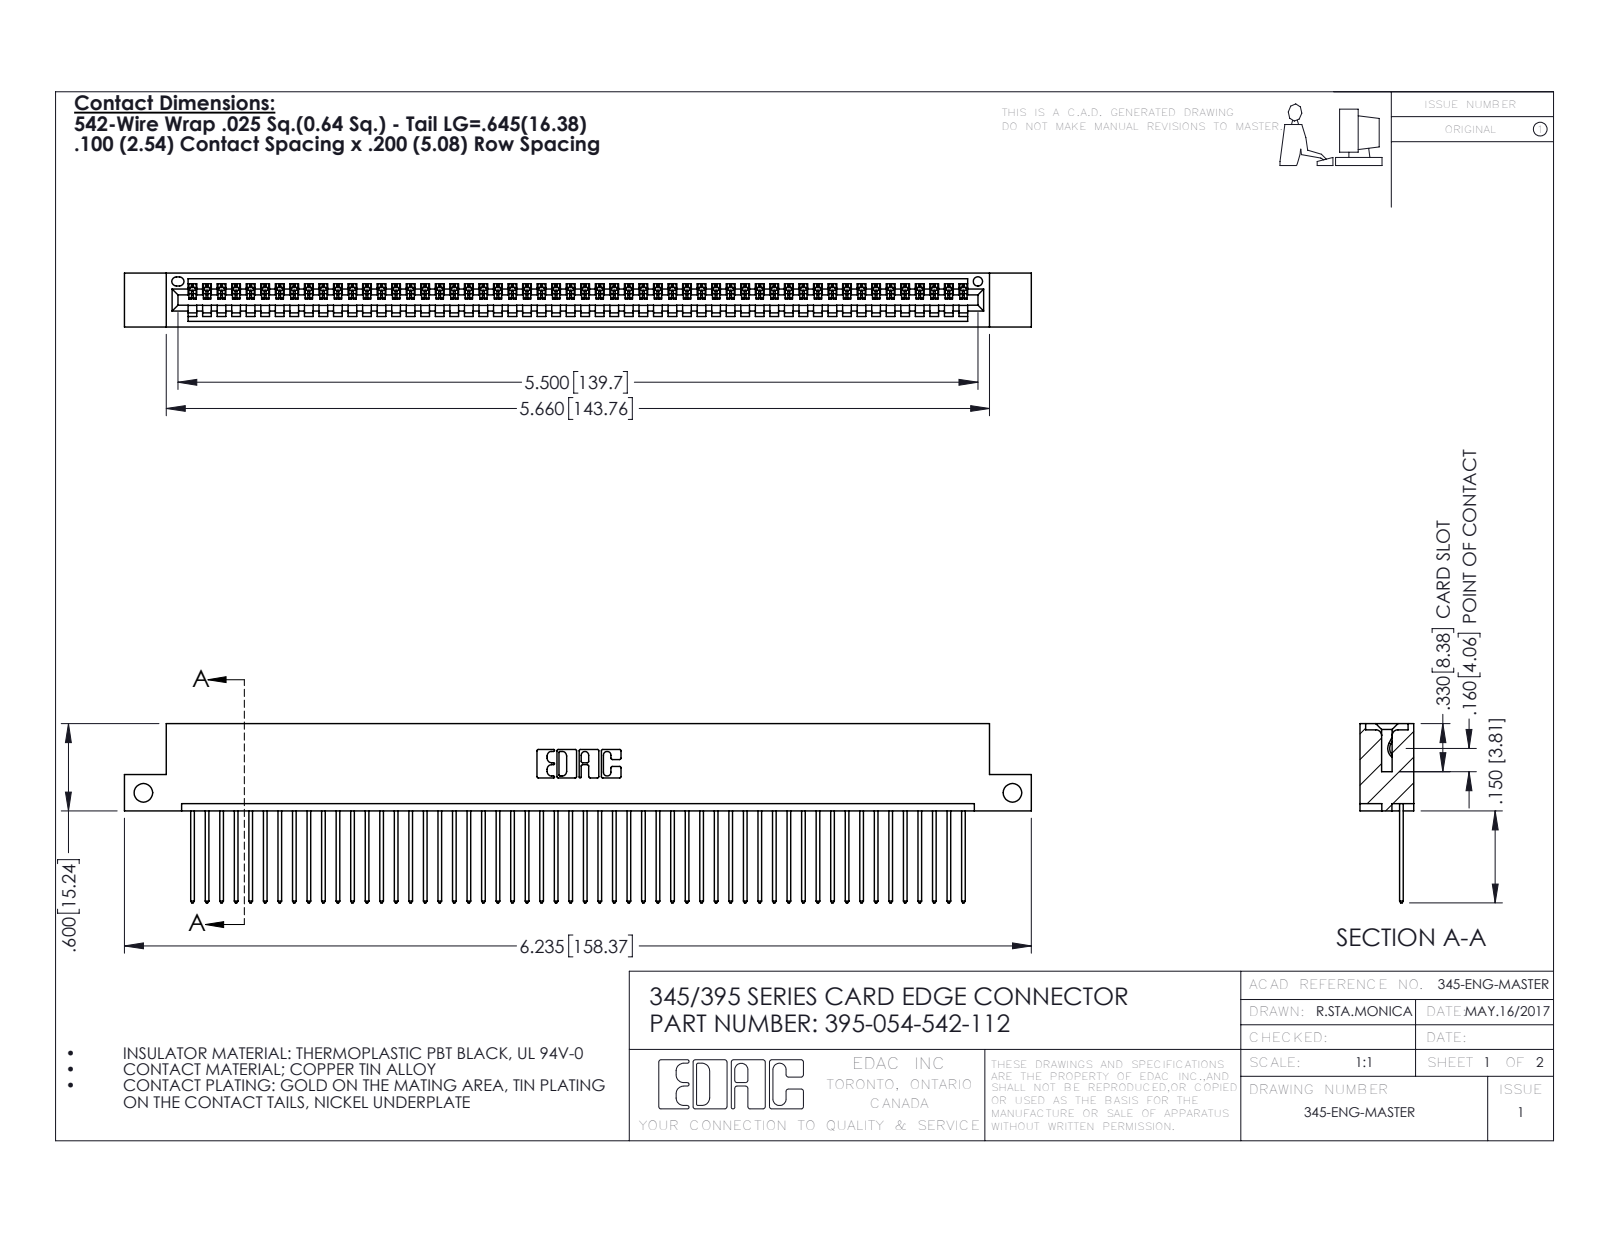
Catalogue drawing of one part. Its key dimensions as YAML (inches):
part_name: "395-054-542-112; 345-292-001_345-293-142; 345 Part_Flush Mounting Lugs - Side Mount"
step_written_by: "SolidWorks 2016 (CONFIG_CONTROL_DESIGN)"
units: inches
bodies: {solids: 55, faces: 3258, planar: 2240, cylindrical: 1018, other: 0}
overall_size: [6.235, 1.232, 0.37]
volume: 0.926
surface_area: 32.46
round_holes:
  - {diameter: 0.128, count: 2}
  - {diameter: 0.064, count: 1}
partial_cylinders:
  - {radius: 0.006, count: 108}
  - {radius: 0.01, count: 108}
  - {radius: 0.01, count: 22}
  - {radius: 0.007, count: 6}
  - {radius: 0.031, count: 6}
  - {radius: 0.026, count: 3}
  - {radius: 0.031, count: 2}
  - {radius: 0.04, count: 2}
face_to_face_distances: [0.072, 0.298, 0.098, 0.272, 0.025, 0.37, 0.2, 0.225, 0.149, 0.072]
hole_center_spacings: [5.975]
